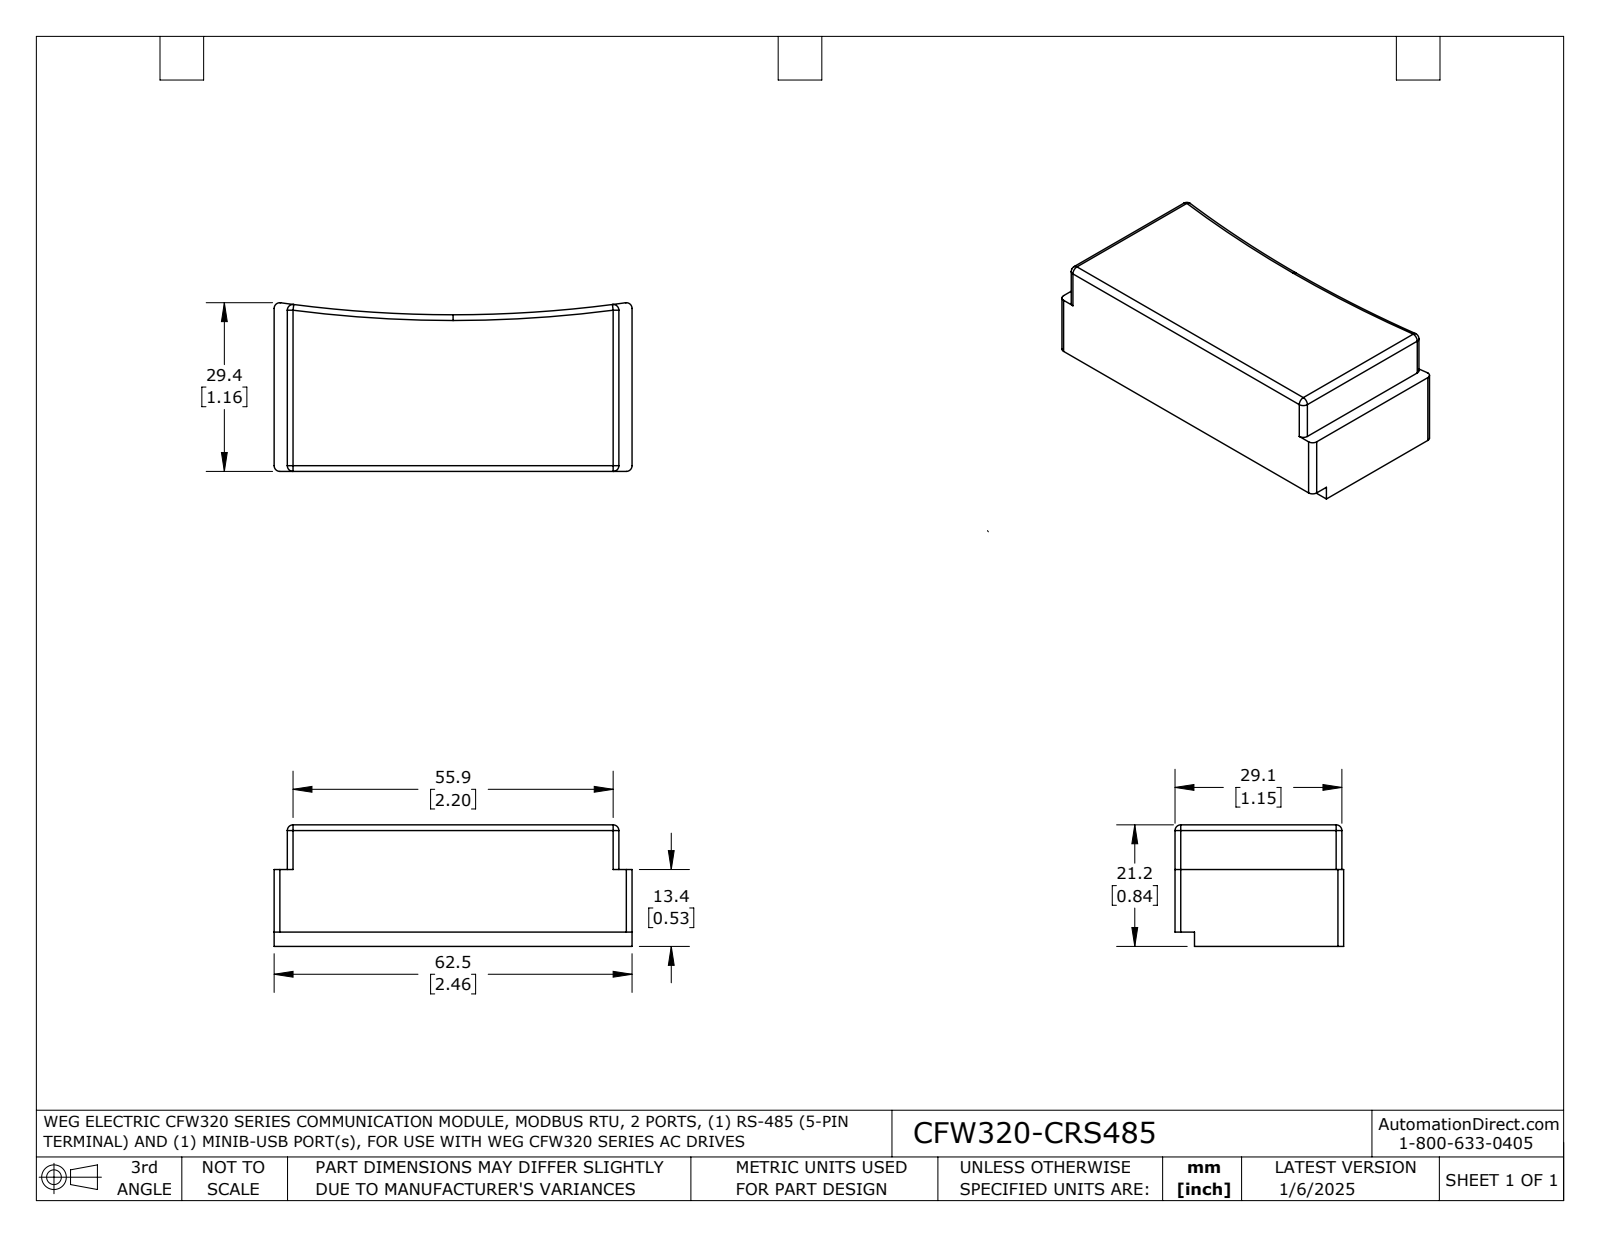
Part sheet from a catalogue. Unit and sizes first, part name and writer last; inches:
Units: inches
Overall size (bounding box): 2.461 × 1.159 × 0.835
Partial cylindrical surfaces — rounded edges, fillets, slot ends (radius × count): R0.039 ×11, R8.543 ×1
Main face-to-face distances: 0.835, 0.091, 2.37, 2.461, 0.098, 0.737, 2.28, 0.134, 0.528, 0.43
Volume: 2.173 in³ · Surface area: 11.18 in²
Bodies: 1 solid, 33 faces (11 planar, 16 cylindrical, 6 other)
Part name (STEP PRODUCT): CFW320-CRS485
STEP written by: SolidWorks 2021 (AUTOMOTIVE_DESIGN)
